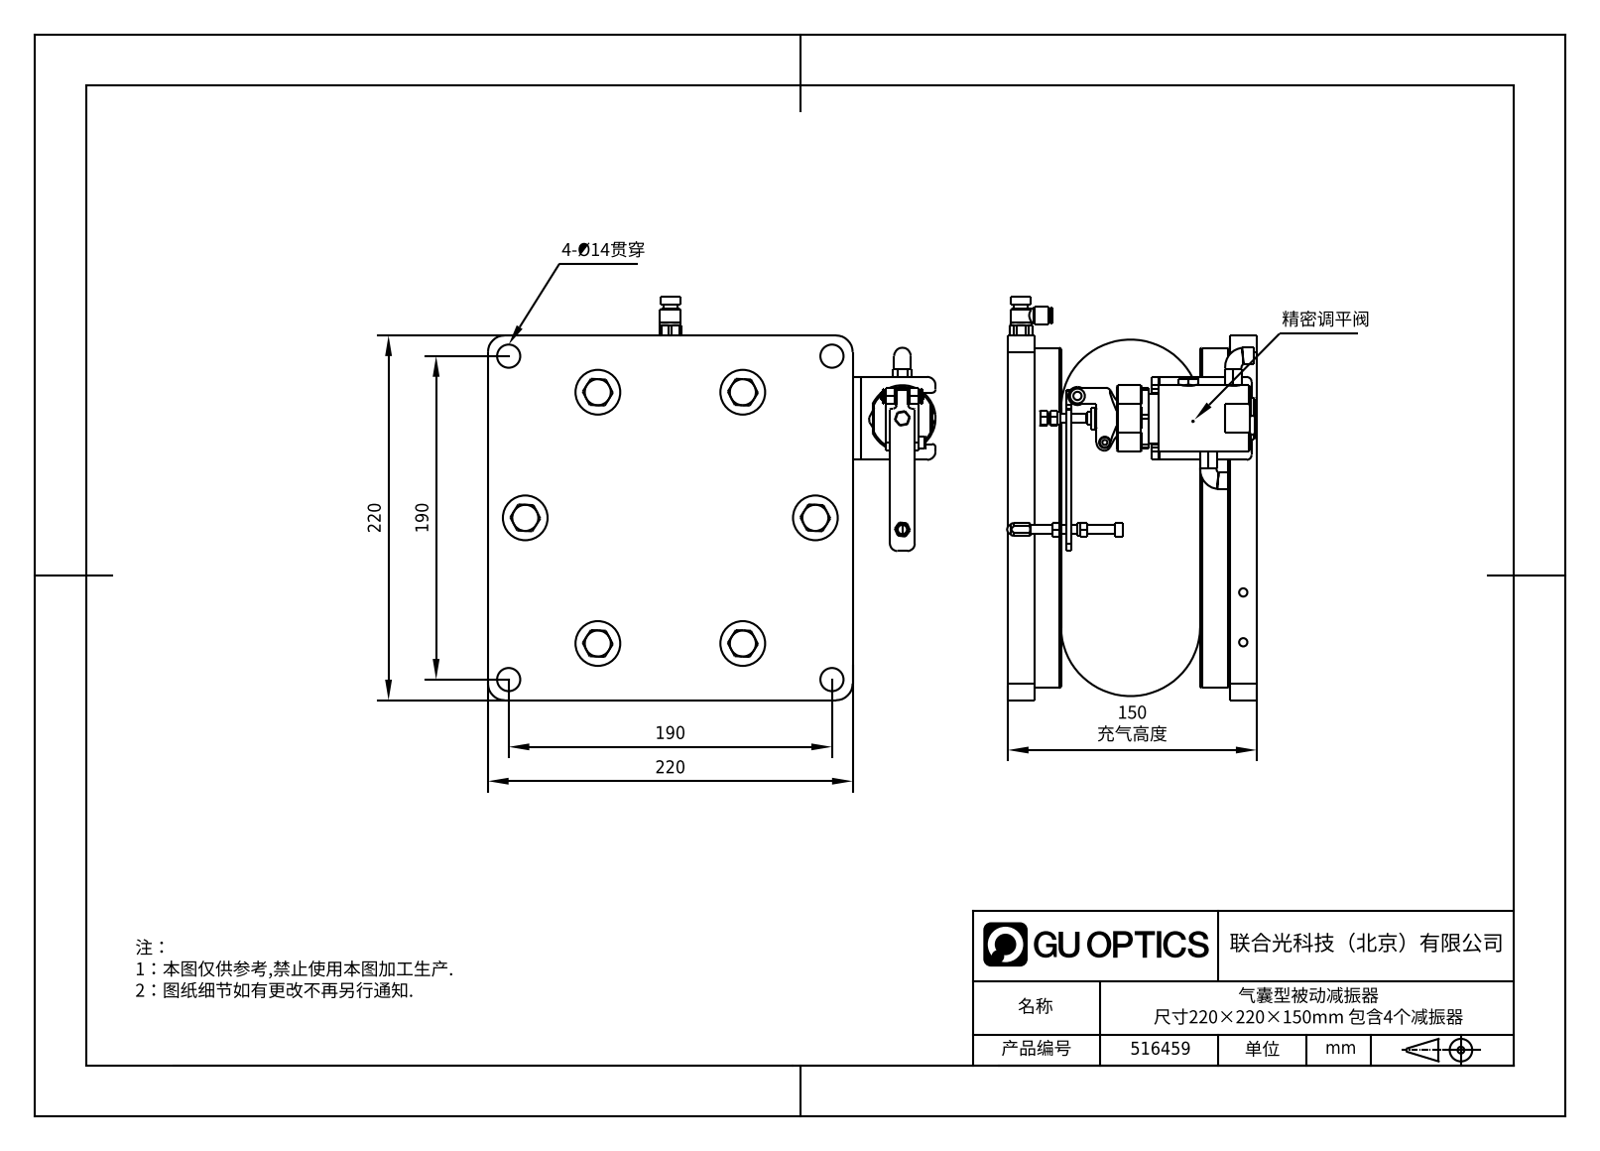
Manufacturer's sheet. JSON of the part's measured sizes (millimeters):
{"part_name": "516459", "step_written_by": "SolidWorks 2020 (CONFIG_CONTROL_DESIGN)", "units": "millimeters", "bodies": {"solids": 0, "faces": 536, "planar": 294, "cylindrical": 124, "other": 118}, "overall_size": [270, 243.5, 150.5], "round_holes": [[27, 6], [14, 4], [5, 3], [11.5, 2], [9.7, 1], [13, 1], [40, 1], [205, 1]], "round_bosses_or_shafts": [[8.5, 7], [10, 3], [8, 3], [7, 2], [5, 2], [30, 1], [12.7, 1], [12.6, 1]], "partial_cylinders_radius": [[0.3, 6], [5, 6], [2, 4], [10, 4], [3, 2], [4.5, 2], [0.74, 1], [4.74, 1]], "face_to_face_distances": [16, 134, 118, 150, 18, 34, 116, 100, 32, 84], "hole_center_spacings": [87.5, 87.49, 98.01, 137.89, 142.91, 151.55, 181.42, 195]}
